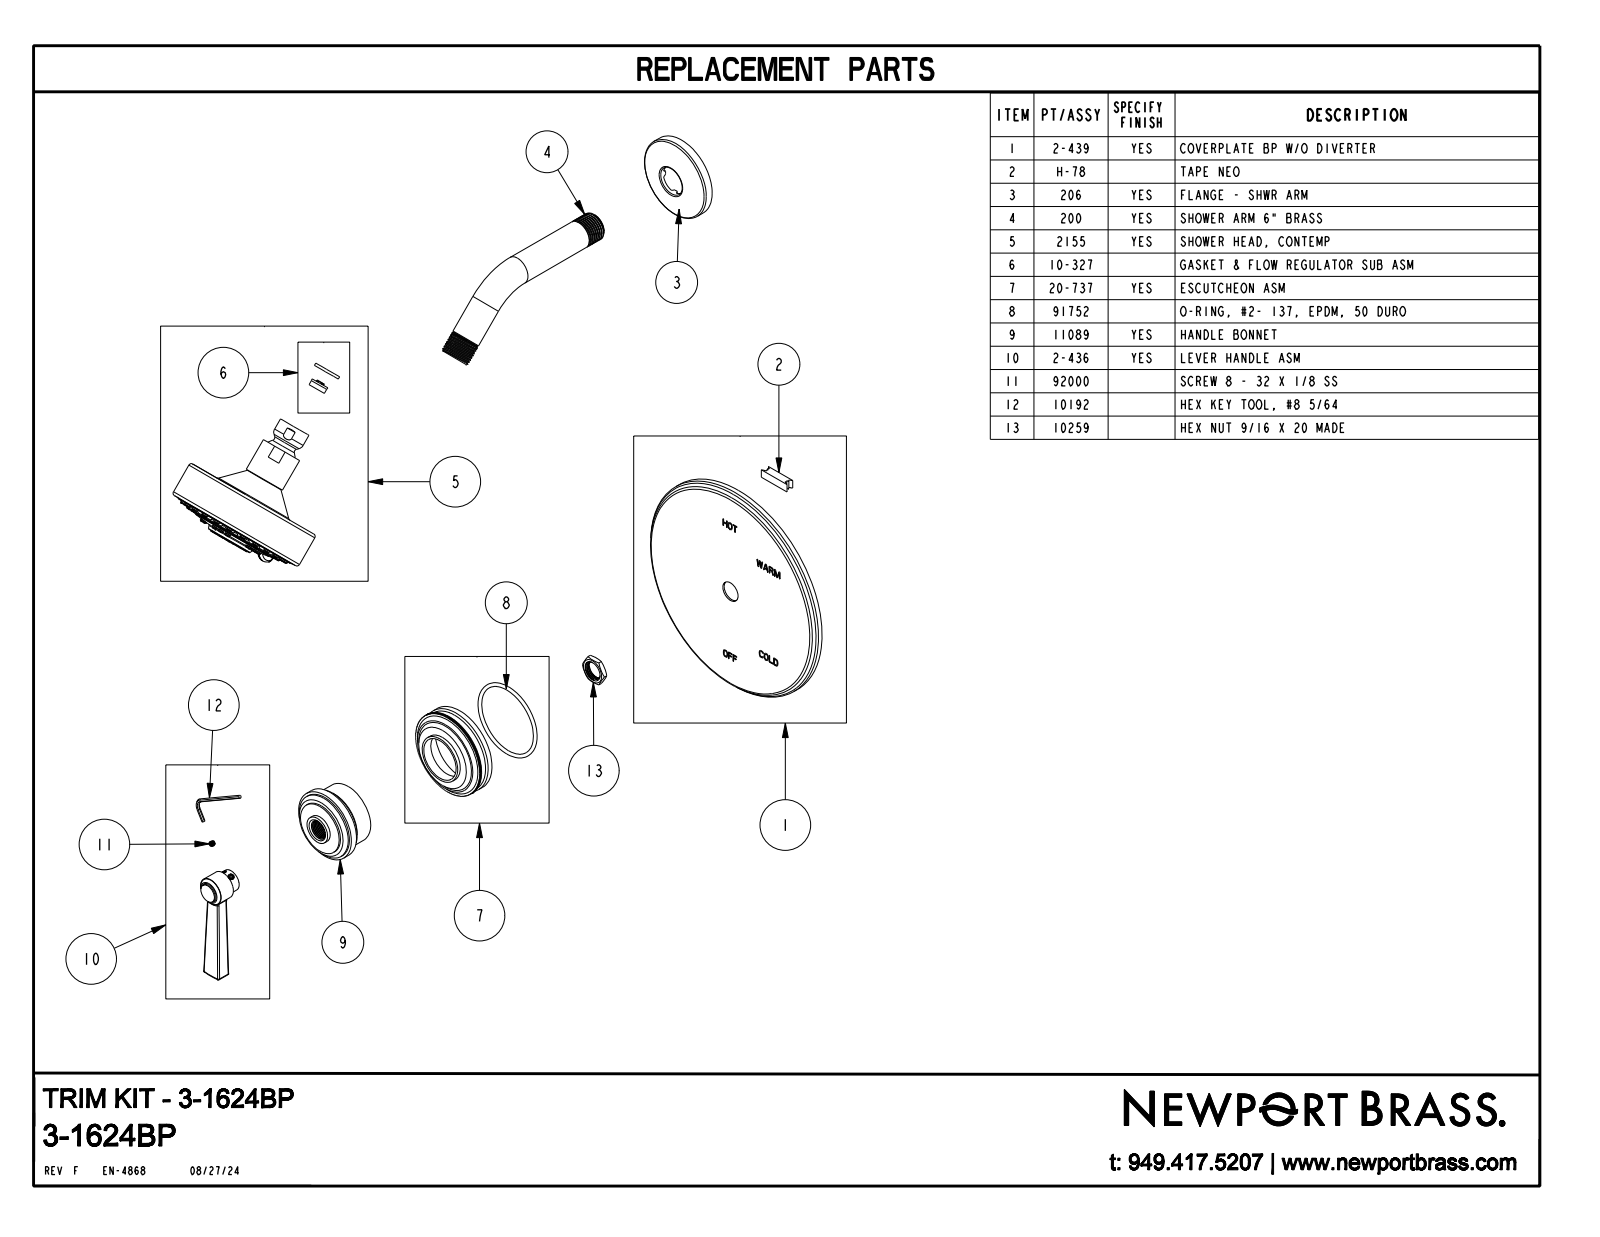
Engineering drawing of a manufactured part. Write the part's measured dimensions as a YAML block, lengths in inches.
part_name: "3-1624BP"
step_written_by: "CREO PARAMETRIC BY PTC INC, 2018400 (CONFIG_CONTROL_DESIGN)"
units: inches
bodies: {solids: 2, faces: 2006, planar: 837, cylindrical: 400, other: 769}
overall_size: [16.44, 8.175, 6.5]
volume: 37.38
surface_area: 164.7
round_holes:
  - {diameter: 0.059, count: 8}
  - {diameter: 0.925, count: 1}
round_bosses_or_shafts:
  - {diameter: 0.142, count: 39}
  - {diameter: 0.165, count: 23}
  - {diameter: 0.813, count: 2}
  - {diameter: 6.5, count: 1}
  - {diameter: 4, count: 1}
  - {diameter: 3.724, count: 1}
  - {diameter: 2.5, count: 1}
  - {diameter: 2.4, count: 1}
partial_cylinders:
  - {radius: 0.079, count: 8}
  - {radius: 0.02, count: 2}
  - {radius: 0.04, count: 2}
  - {radius: 0.055, count: 2}
  - {radius: 0.138, count: 1}
  - {radius: 0.472, count: 1}
  - {radius: 0.512, count: 1}
  - {radius: 0.63, count: 1}
face_to_face_distances: [0.313, 2.088, 1.775, 0.2, 0.1, 1.147, 1.3, 0.15, 0.4, 1.375]
hole_center_spacings: [0.443, 0.579, 0.818, 0.819, 1.069, 0.443, 0.578, 1.069]
